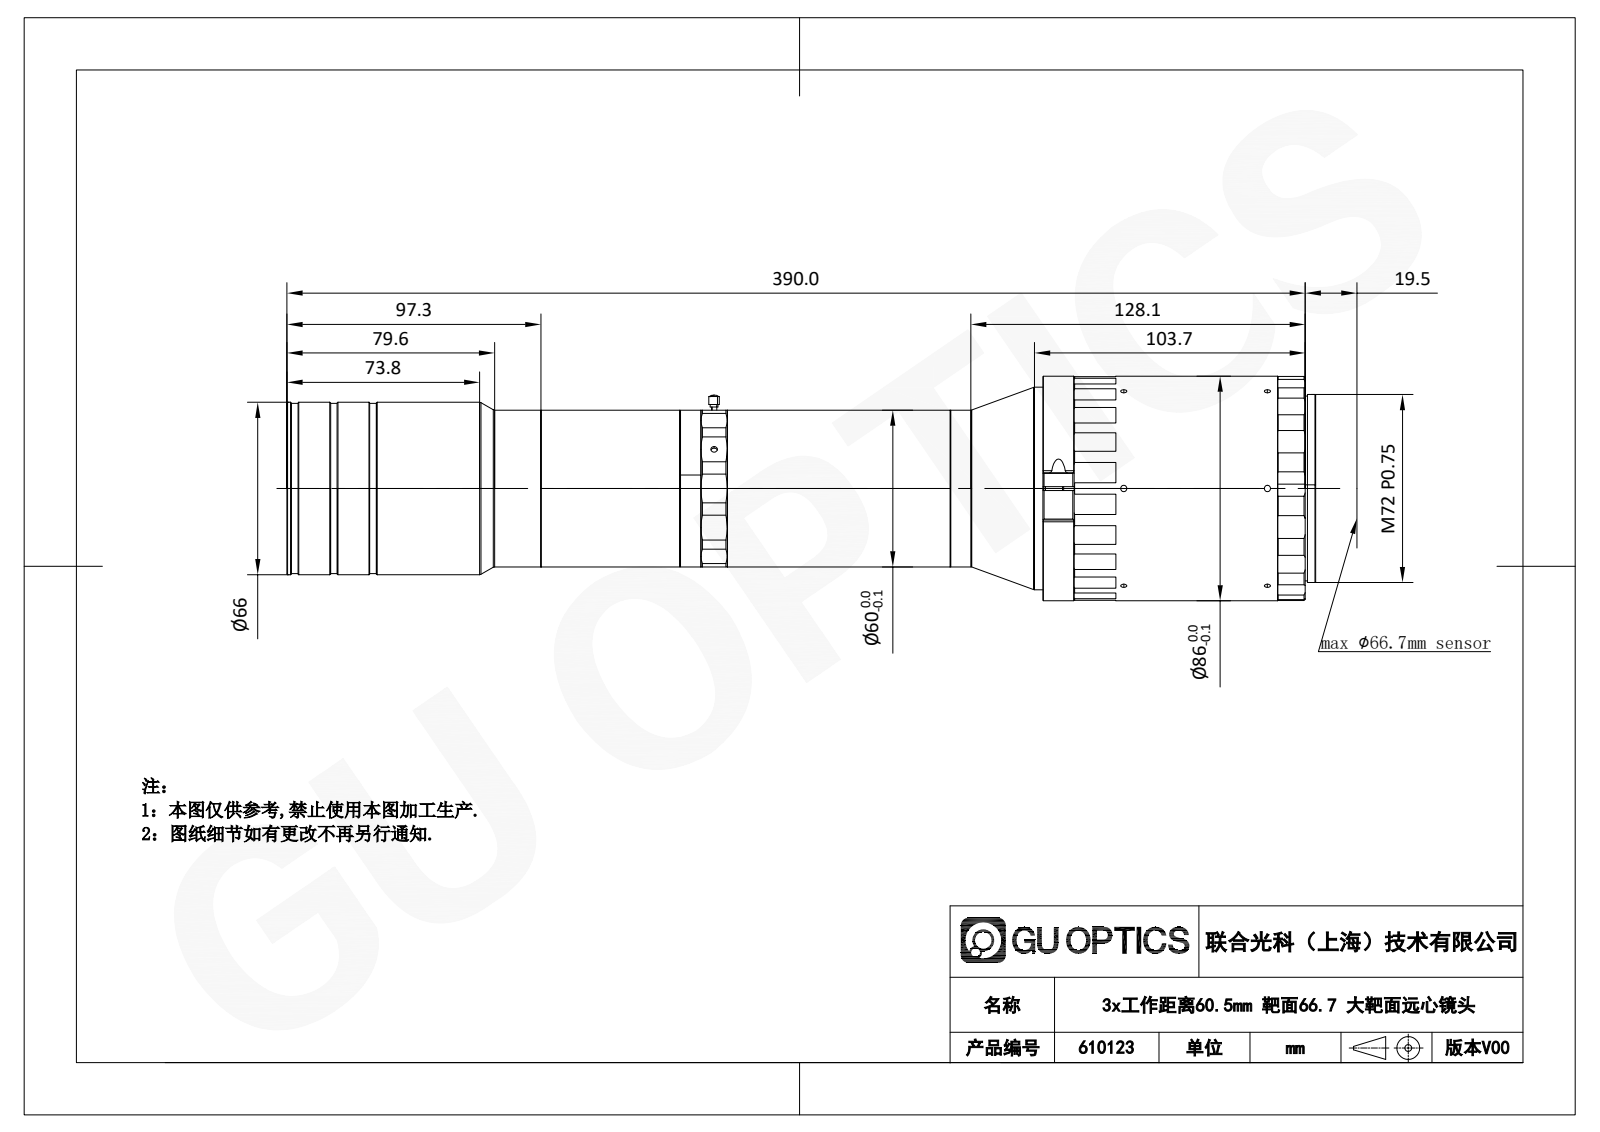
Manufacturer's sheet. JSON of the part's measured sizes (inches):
{"part_name": "DTCA150M-22.4-G-M72-AL-19.5", "step_written_by": "SolidWorks 2017 (CONFIG_CONTROL_DESIGN)", "units": "inches", "bodies": {"solids": 1, "faces": 528, "planar": 130, "cylindrical": 189, "other": 209}, "overall_size": [15.511, 3.641, 3.386], "volume_in3": 85.01, "surface_area_in2": 168.7, "round_holes": [[0.094, 6], [0.098, 3], [0.087, 1], [0.134, 1], [0.177, 1], [2.343, 1], [2.618, 1], [2.677, 1], [2.854, 1], [3.11, 1], [3.189, 1], [3.24, 1]], "round_bosses_or_shafts": [[3.386, 1], [3.228, 1], [3.051, 1], [2.835, 1], [2.787, 1], [2.598, 1], [2.567, 1], [2.362, 1]], "partial_cylinders_radius": [[0.591, 38], [0.039, 2], [0.157, 1], [1.201, 1], [1.949, 1]], "face_to_face_distances": [0.74, 3.217, 3.957, 2.362, 11.396, 14.613, 15.353, 14.625, 3.228, 0.728], "hole_center_spacings": [2.165, 5.492]}
